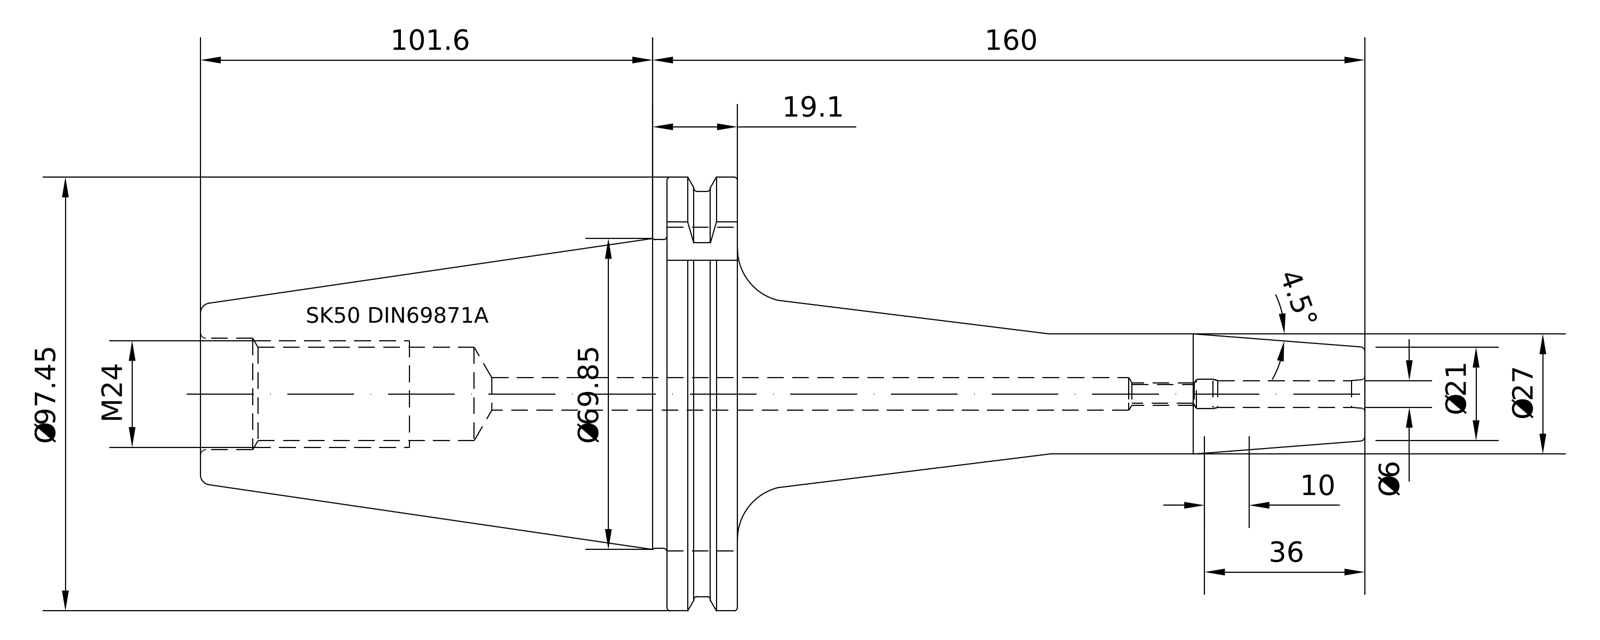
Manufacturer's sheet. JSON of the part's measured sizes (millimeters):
{"part_name": "50-442-06", "step_written_by": "PRO/ENGINEER BY PARAMETRIC TECHNOLOGY CORPORATION, 2010430 (CONFIG_CONTROL_DESIGN)", "units": "millimeters", "bodies": {"solids": 1, "faces": 95, "planar": 21, "cylindrical": 24, "other": 50}, "overall_size": [261.6, 97.47, 94], "volume_mm3": 441057, "surface_area_mm2": 54730, "round_holes": [[6, 1], [20.75, 1], [25.01, 1], [25.7, 1]], "round_bosses_or_shafts": [[91, 1], [69.15, 1], [27, 1], [24.01, 1]], "partial_cylinders_radius": [[1.75, 1], [48.74, 1]], "face_to_face_distances": [15.85, 72.8, 104.8, 120.65, 25.8, 261.6, 156.8, 140.95, 48, 56.8]}
